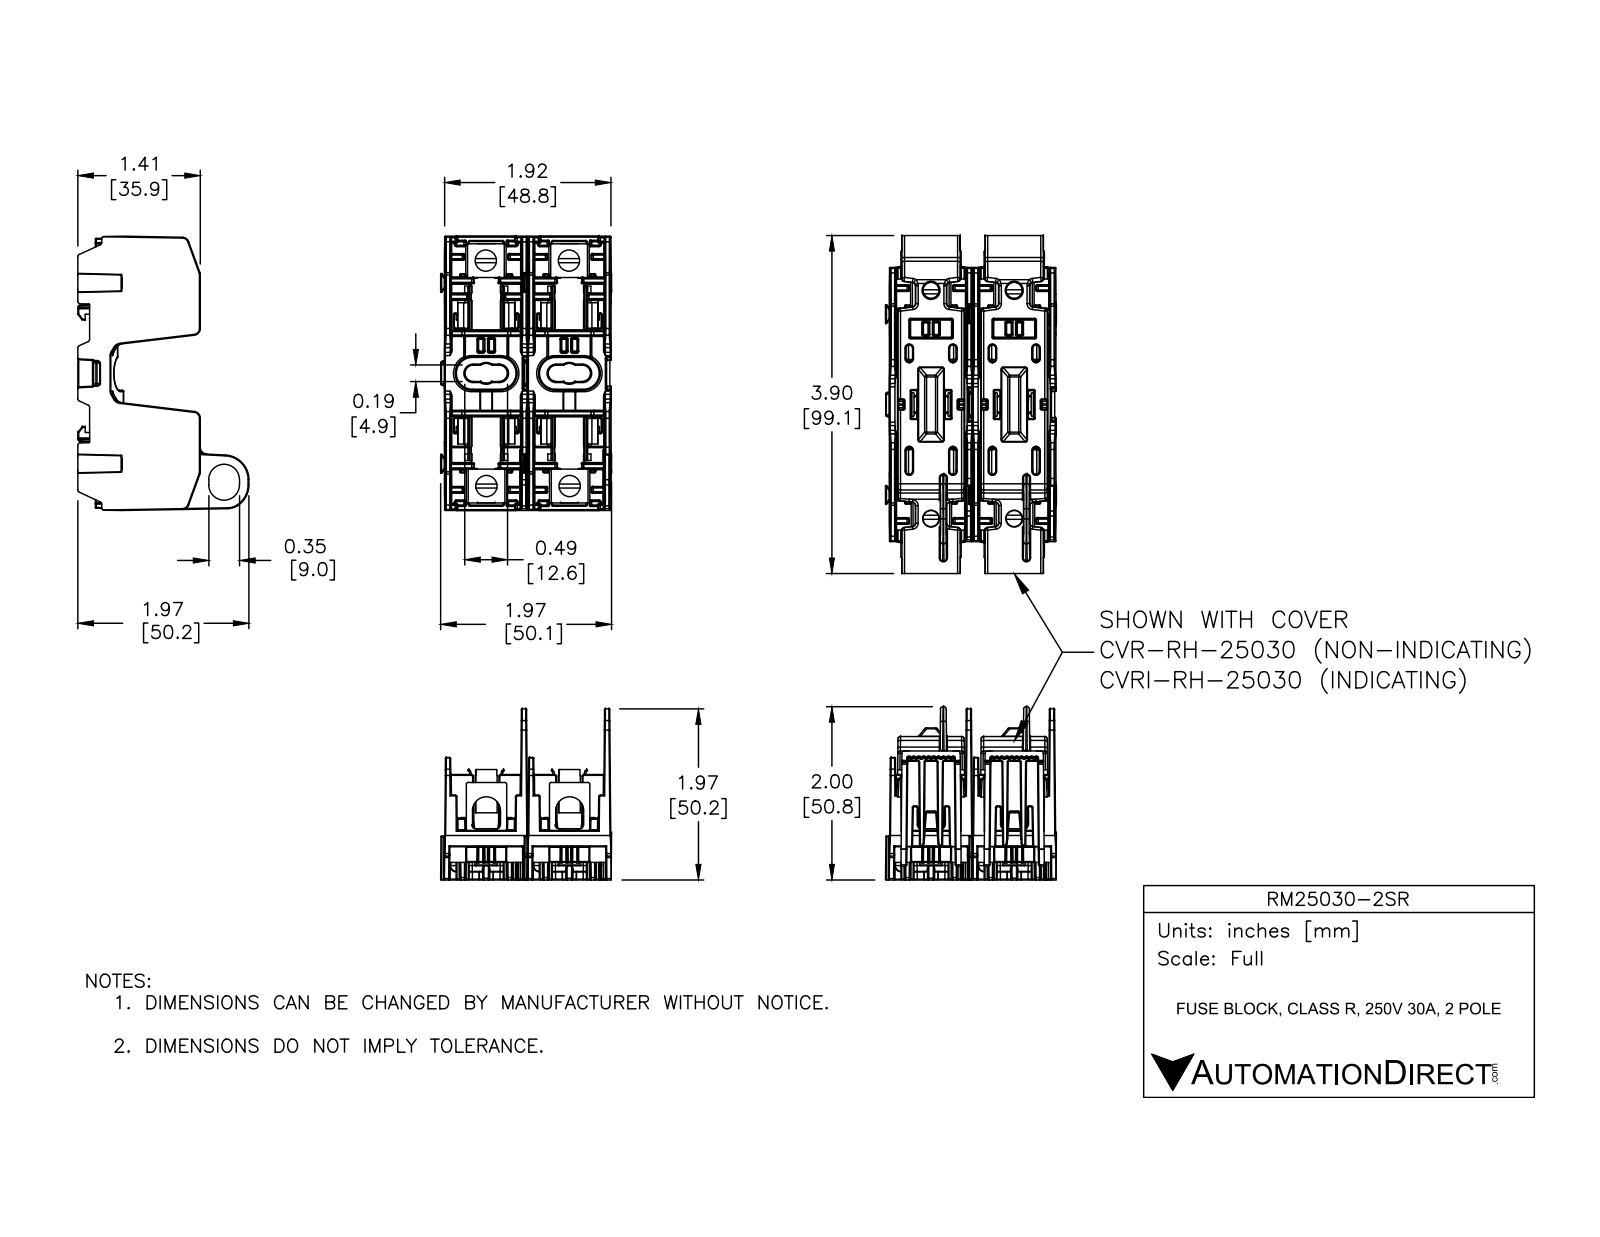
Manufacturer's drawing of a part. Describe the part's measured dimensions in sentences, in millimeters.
The part is named "RM25030-1SR; RM25030-2SR". Its 3-D file was written by "SolidWorks 2016 (AUTOMOTIVE_DESIGN)". It is 22 solids with 5802 faces: 1300 planar, 2460 cylindrical and 2042 other. Overall it measures 80.4 by 50.2 by 50.1 millimeters. Its volume is 46 560 cubic millimeters and its surface area 48 520 square millimeters. Round holes: 4 of diameter 3.6, 4 of diameter 6.2. Round bosses or shafts: 4 of diameter 6.2. Partial cylindrical surfaces (rounded edges, fillets, slot ends): 785 of radius 0.3, 488 of radius 0.2, 134 of radius 0.5, 32 of radius 0.5, 27 of radius 2, 21 of radius 1.1, 20 of radius 0.8, 14 of radius 1.8. The main face-to-face distances are 24.5, 22.4, 0.6, 2.1, 46.9, 1.5, 8.7, 9.4, 20.9, 0.4. The hole center spacings are 14, 24.5, 52, 28.2, 28.3, 38, 45.2, 57.5.
